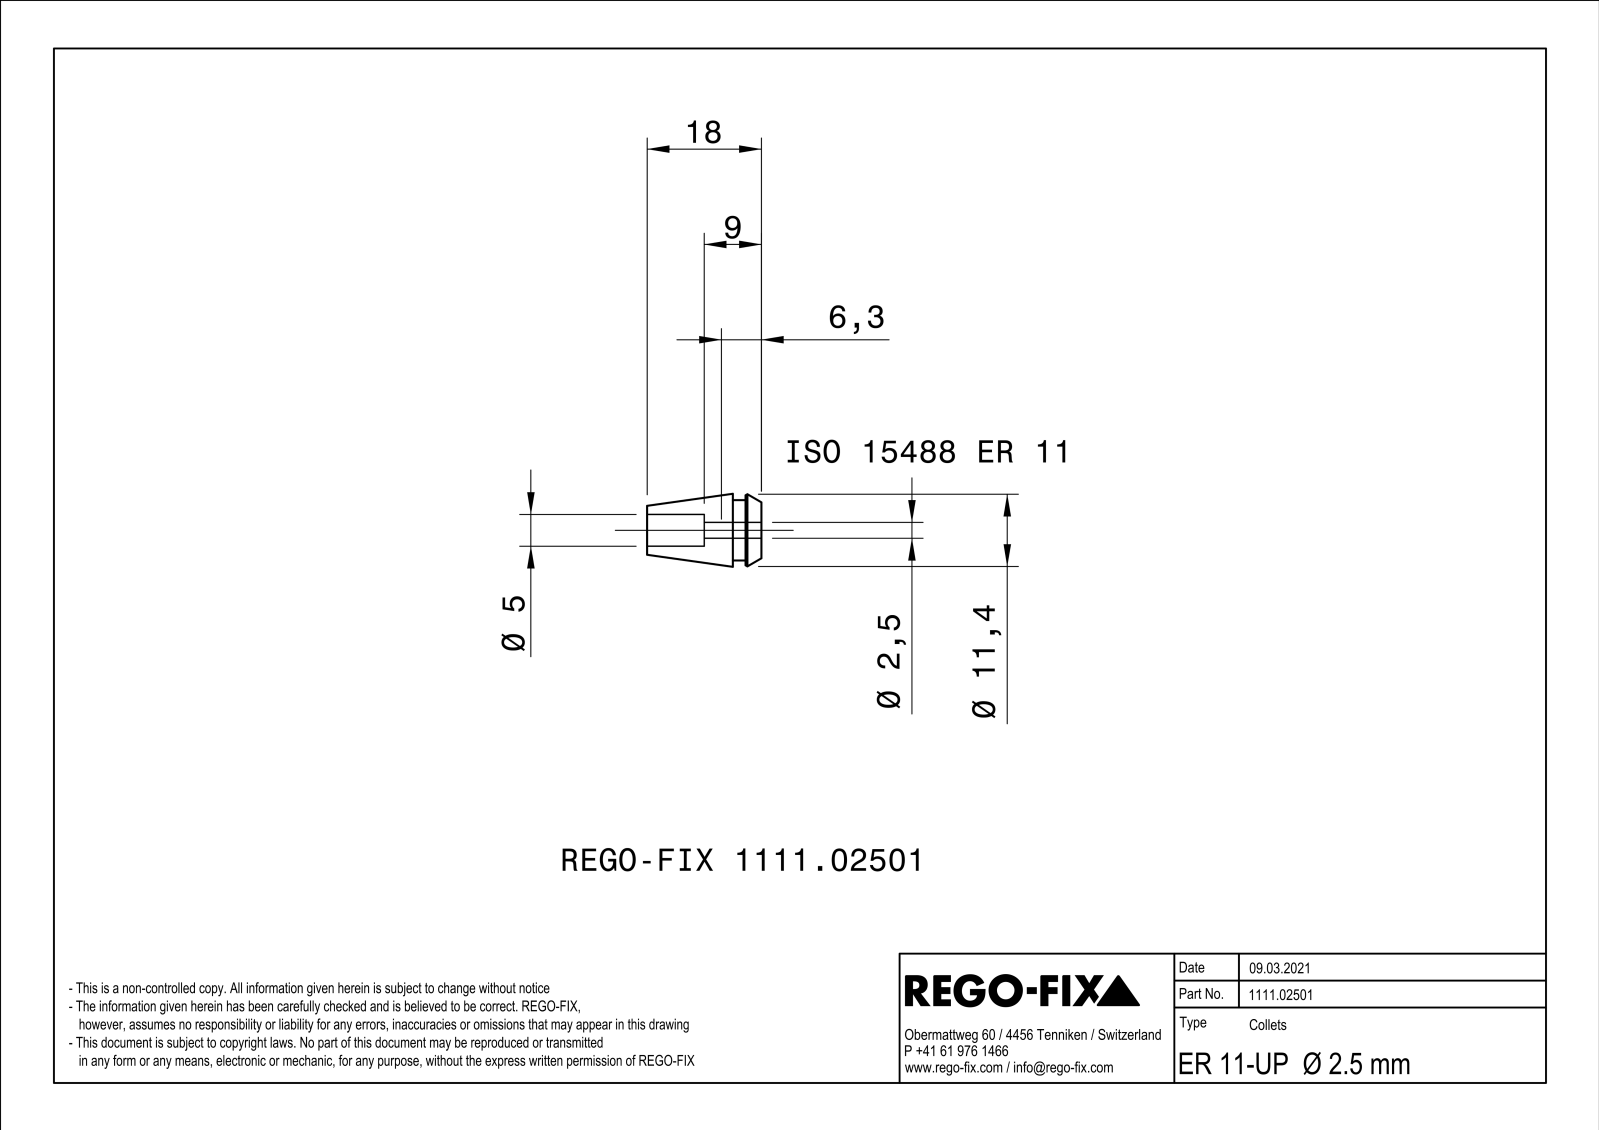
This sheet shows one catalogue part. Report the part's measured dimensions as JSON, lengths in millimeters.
{"part_name": "NOCUT", "step_written_by": "SIEMENS PLM Software Solid Edge ST10 (AUTOMOTIVE_DESIGN)", "units": "millimeters", "bodies": {"solids": 1, "faces": 268, "planar": 108, "cylindrical": 52, "other": 108}, "overall_size": [18, 11.49, 11.49], "volume_mm3": 841, "surface_area_mm2": 2006, "round_bosses_or_shafts": [[11.5, 1]], "partial_cylinders_radius": [[25, 4], [1.25, 1], [2.5, 1], [4.75, 1]], "face_to_face_distances": [0.46, 0.45, 0.44, 3.28, 3.72, 4.5, 2.5, 2, 15.5, 7]}
